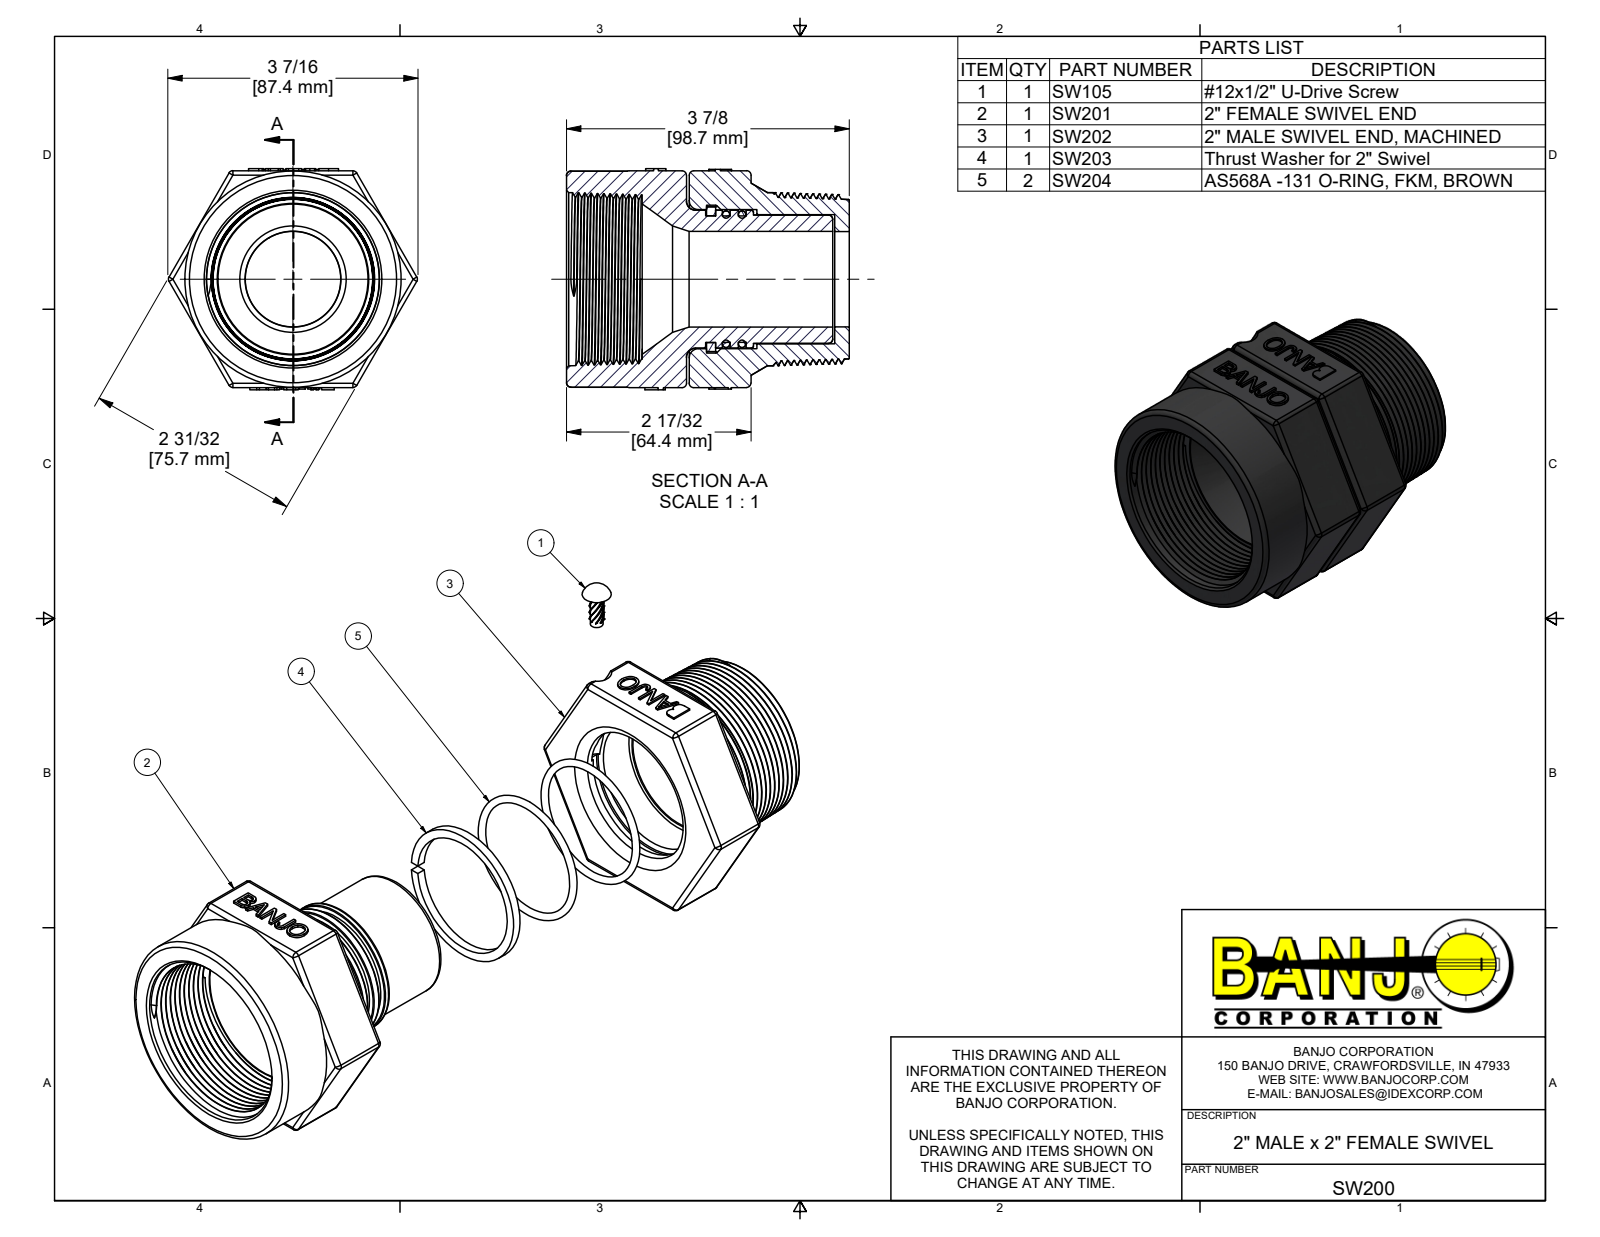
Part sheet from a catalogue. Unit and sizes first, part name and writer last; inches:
Units: inches
Overall size (bounding box): 3.887 × 3.422 × 3.04
Round holes (diameter × count): ⌀0.196 ×1, ⌀0.413 ×1, ⌀1.31 ×1, ⌀1.315 ×1, ⌀1.74 ×1, ⌀1.775 ×1, ⌀1.913 ×1, ⌀2.033 ×1
Round bosses / shafts (diameter × count): ⌀2.97 ×1, ⌀2.38 ×1, ⌀1.99 ×1, ⌀1.898 ×1, ⌀1.765 ×1, ⌀1.743 ×1, ⌀1.737 ×1, ⌀0.202 ×1
Partial cylindrical surfaces — rounded edges, fillets, slot ends (radius × count): R0.06 ×18, R0.062 ×18, R0.013 ×8, R0.611 ×1, R0.659 ×1
Main face-to-face distances: 2.98, 0.037, 2.237, 2.2, 0.887, 0.85, 1.65, 1.687, 3.887, 2.537
Volume: 15.55 in³ · Surface area: 120.3 in²
Bodies: 6 solids, 493 faces (197 planar, 80 cylindrical, 216 other)
Part name (STEP PRODUCT): SW200; SW201; SW202; SWX202 (+3 more)
STEP written by: Autodesk Inventor 2022 (AUTOMOTIVE_DESIGN)
